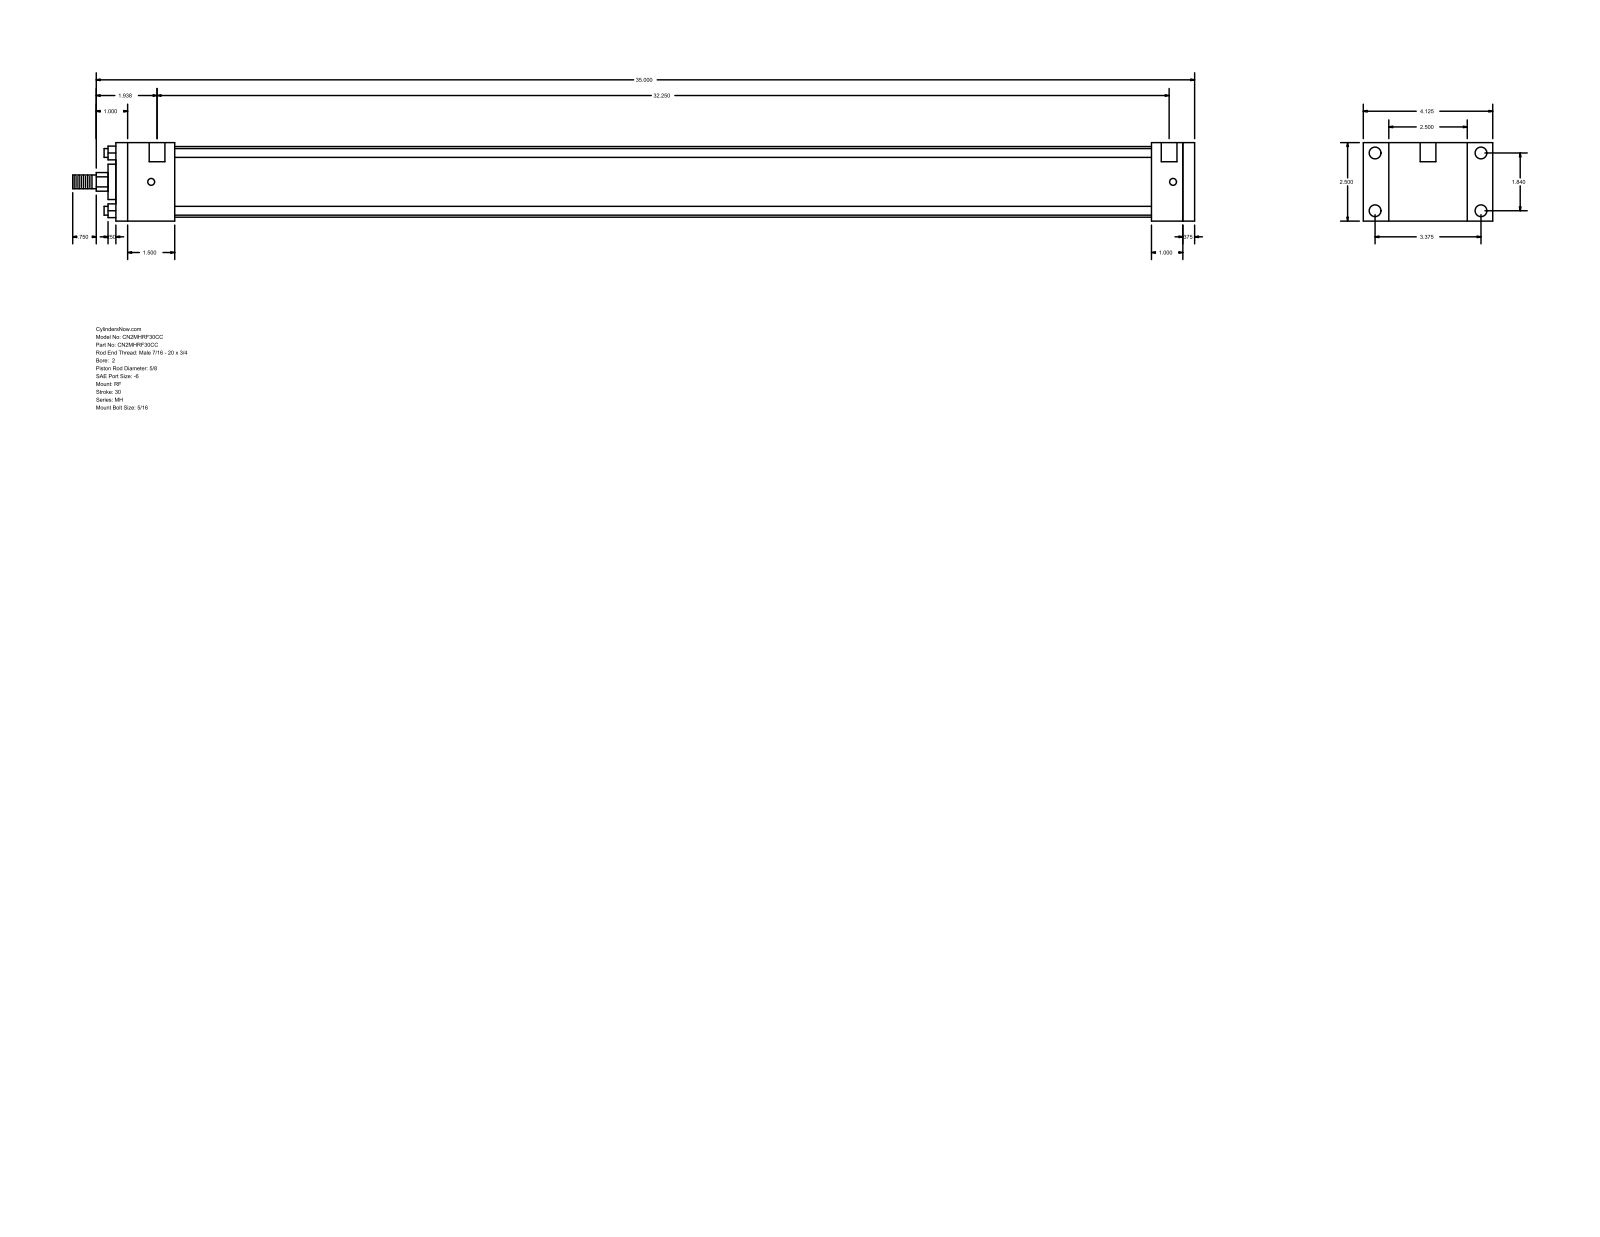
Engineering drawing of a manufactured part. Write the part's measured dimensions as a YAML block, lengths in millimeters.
part_name: "MH_RF__0200_0.625"
step_written_by: "GSSL Pune (CONFIG_CONTROL_DESIGN)"
units: millimeters
bodies: {solids: 0, faces: 92, planar: 64, cylindrical: 28, other: 0}
overall_size: [908.05, 104.78, 63.5]
round_holes:
  - {diameter: 5.56, count: 4}
  - {diameter: 9.53, count: 4}
  - {diameter: 12.7, count: 2}
round_bosses_or_shafts:
  - {diameter: 7.14, count: 4}
  - {diameter: 57.15, count: 1}
  - {diameter: 28.57, count: 1}
  - {diameter: 15.88, count: 1}
  - {diameter: 11.11, count: 1}
partial_cylinders:
  - {radius: 7.54, count: 1}
face_to_face_distances: [63.5, 873.12, 863.6, 9.52, 25.4, 47.62, 838.2, 790.58, 815.98, 825.5]
hole_center_spacings: [46.74, 85.72, 97.63, 827.09, 3.18, 4.76, 819.15, 822.33]
